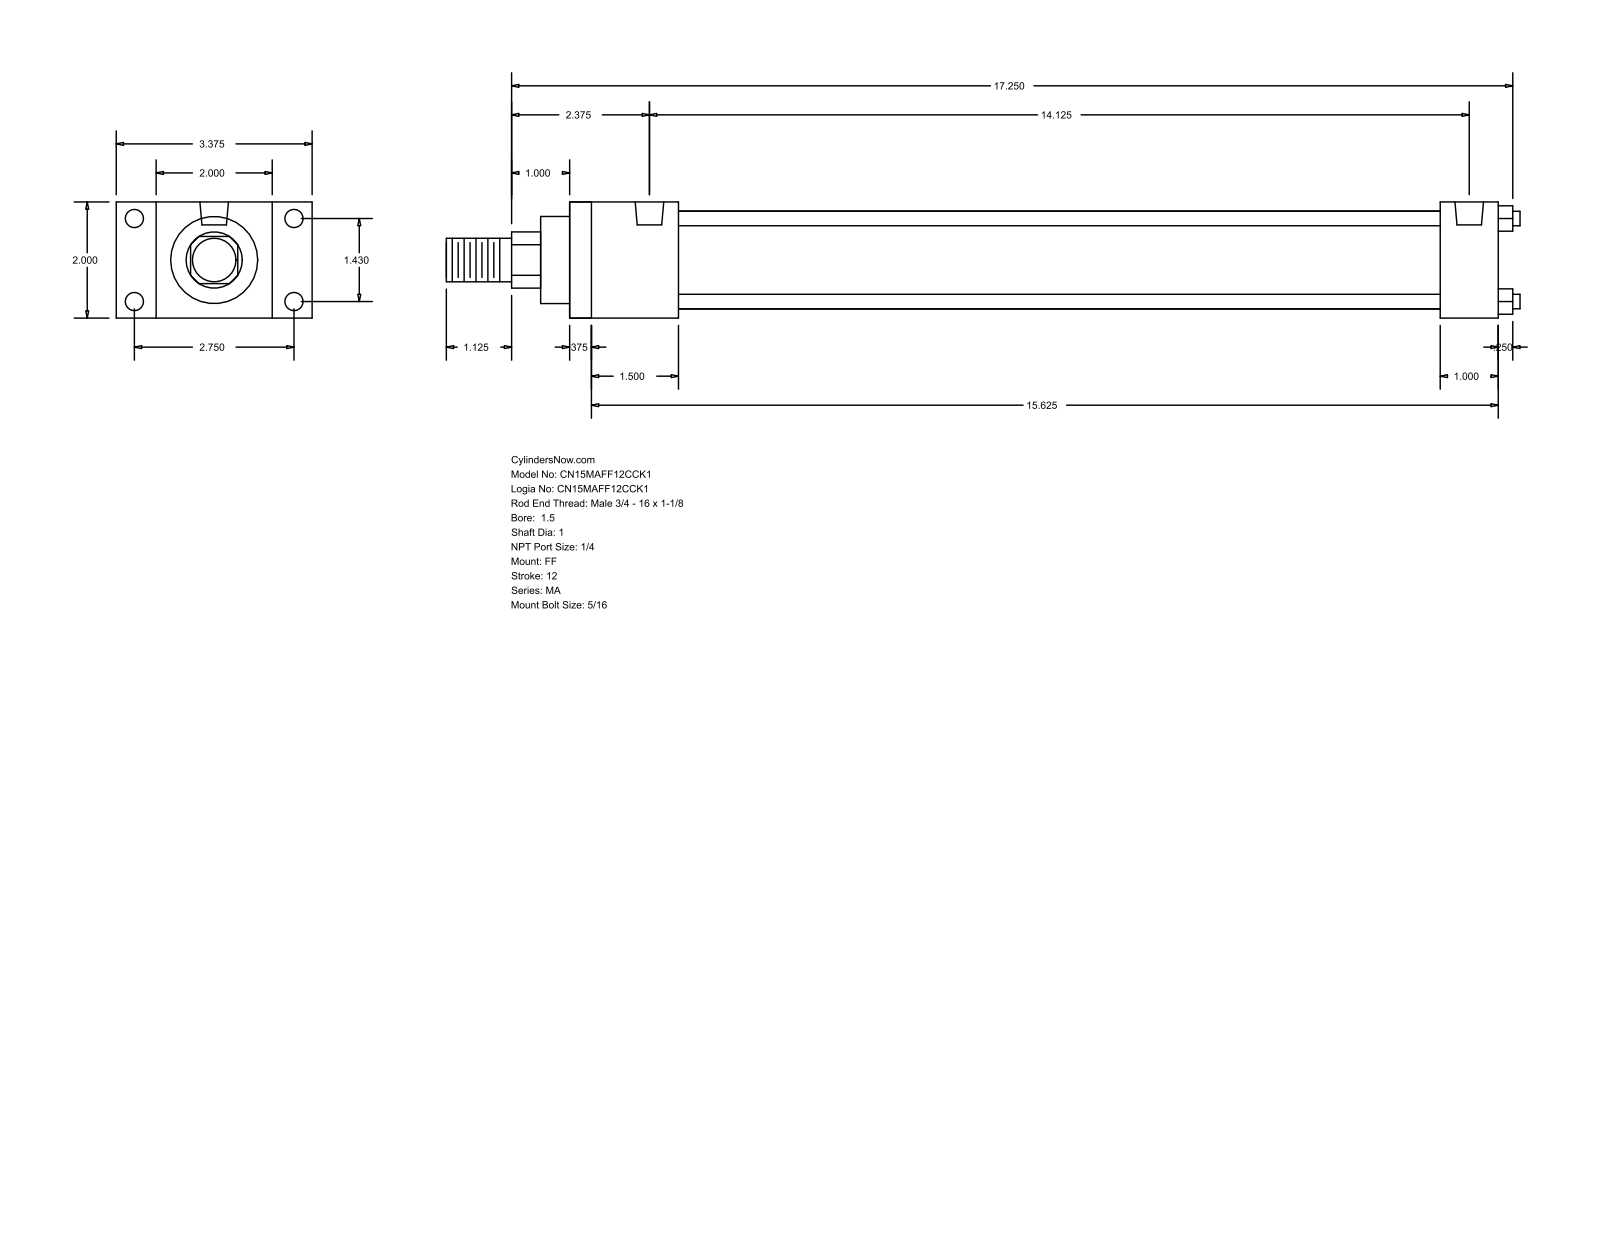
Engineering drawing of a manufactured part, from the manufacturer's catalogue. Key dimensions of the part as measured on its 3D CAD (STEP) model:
Part name (STEP PRODUCT): MA_FF__0150_1
STEP written by: GSSL Pune (CONFIG_CONTROL_DESIGN)
Units: millimetres
Bodies: 0 solids, 92 faces (64 planar, 28 cylindrical, 0 other)
Overall size (bounding box): 469.9 × 85.72 × 50.8
Round holes (diameter × count): ⌀7.94 ×8, ⌀12.49 ×2
Round bosses / shafts (diameter × count): ⌀6.35 ×4, ⌀42.93 ×1, ⌀38.1 ×1, ⌀25.4 ×1, ⌀19.05 ×1
Partial cylindrical surfaces — rounded edges, fillets, slot ends (radius × count): R12.29 ×1
Main face-to-face distances: 50.8, 406.4, 9.52, 396.88, 25.4, 47.63, 381, 38.11, 371.48, 333.37
Hole centre spacings: 36.32, 69.84, 78.72, 358.77
